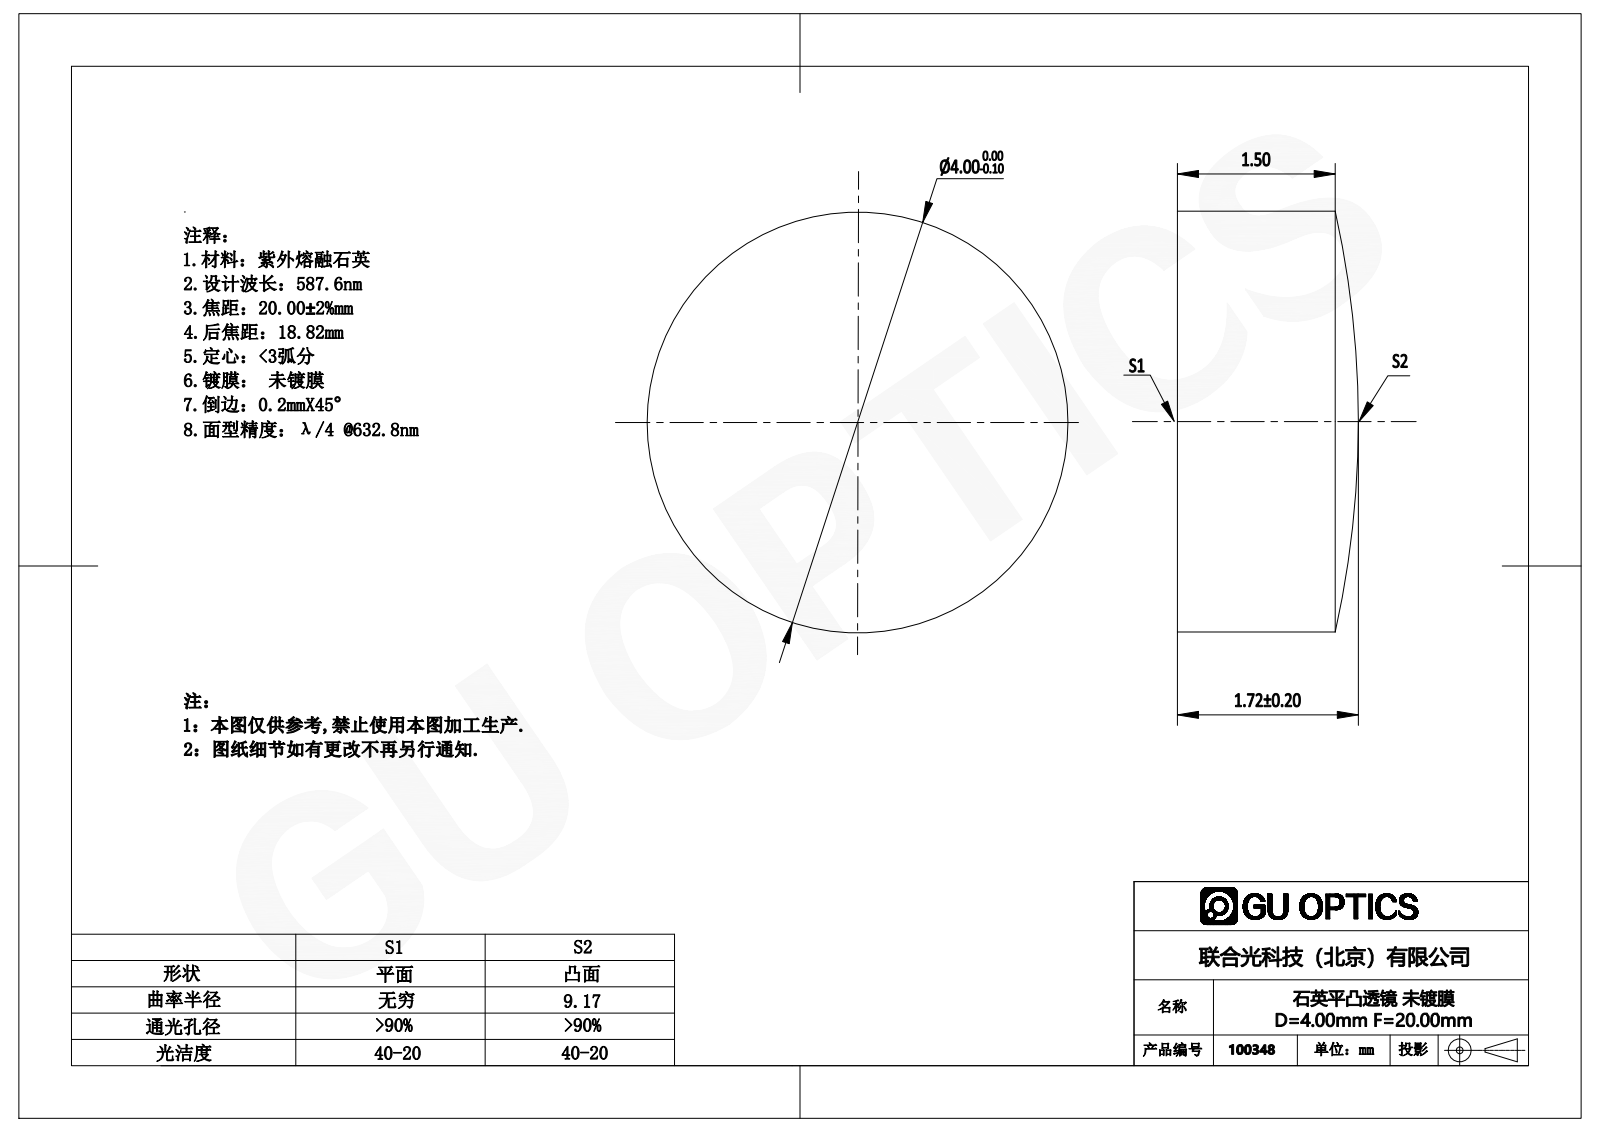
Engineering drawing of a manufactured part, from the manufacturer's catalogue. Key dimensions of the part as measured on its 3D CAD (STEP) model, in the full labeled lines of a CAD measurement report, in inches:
Part name (STEP PRODUCT): 100348
STEP written by: SolidWorks 2016 (AUTOMOTIVE_DESIGN)
Units: inches
Bodies: 1 solid, 5 faces (1 planar, 2 cylindrical, 2 other)
Overall size (bounding box): 0.157 × 0.157 × 0.068
Volume: 0.001 in³ · Surface area: 0.068 in²
Round bosses / shafts (diameter × count): ⌀0.157 ×1
